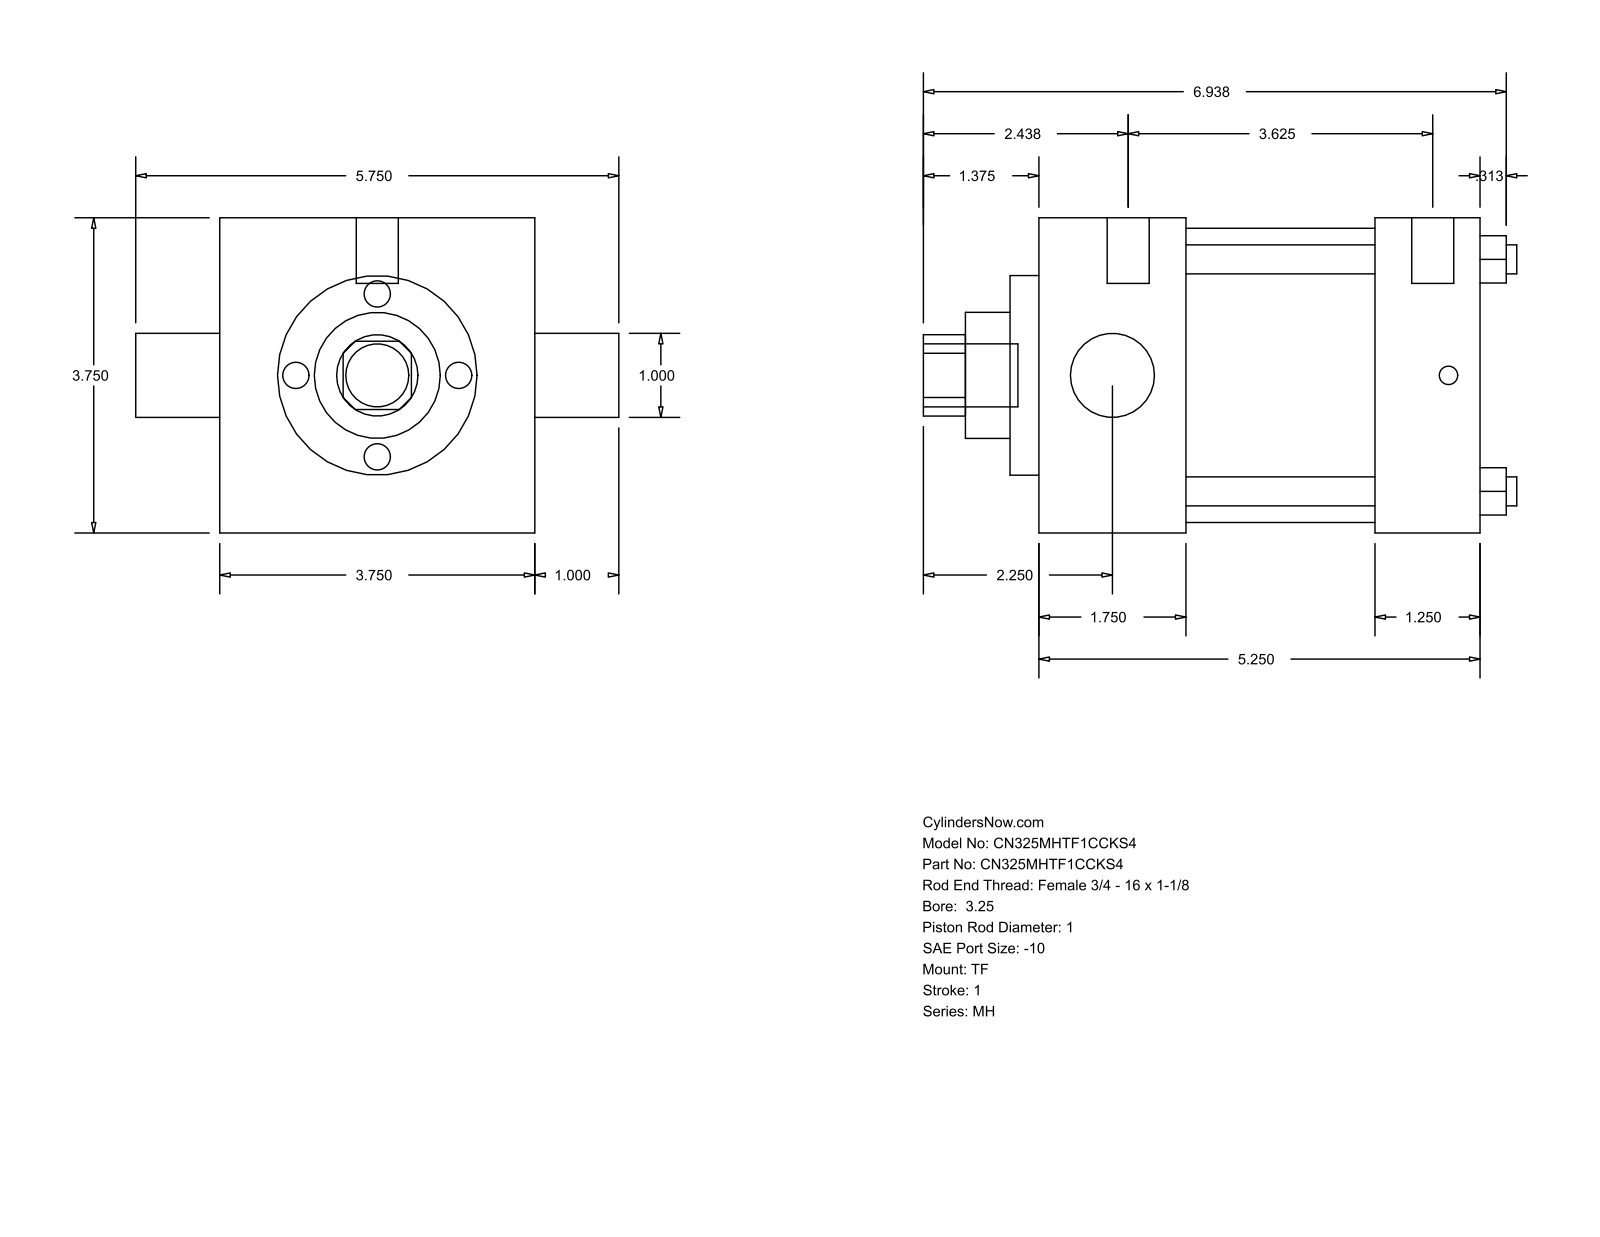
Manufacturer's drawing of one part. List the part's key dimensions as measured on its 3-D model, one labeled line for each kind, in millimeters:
Part name (STEP PRODUCT): MH_TF__0325_1
STEP written by: GSSL Pune (CONFIG_CONTROL_DESIGN)
Units: millimetres
Bodies: 0 solids, 86 faces (61 planar, 25 cylindrical, 0 other)
Overall size (bounding box): 179.39 × 146.05 × 95.25
Round holes (diameter × count): ⌀8.76 ×4, ⌀25.4 ×2, ⌀38.1 ×1, ⌀60.33 ×1, ⌀88.9 ×1
Round bosses / shafts (diameter × count): ⌀5.56 ×3, ⌀12.7 ×2, ⌀19.05 ×1
Partial cylindrical surfaces — rounded edges, fillets, slot ends (radius × count): R12.29 ×1
Main face-to-face distances: 95.24, 133.36, 44.46, 101.61, 57.15, 88.9, 31.75, 8.73, 53.19, 110.34
Hole centre spacings: 49.57, 70.1, 99.14
